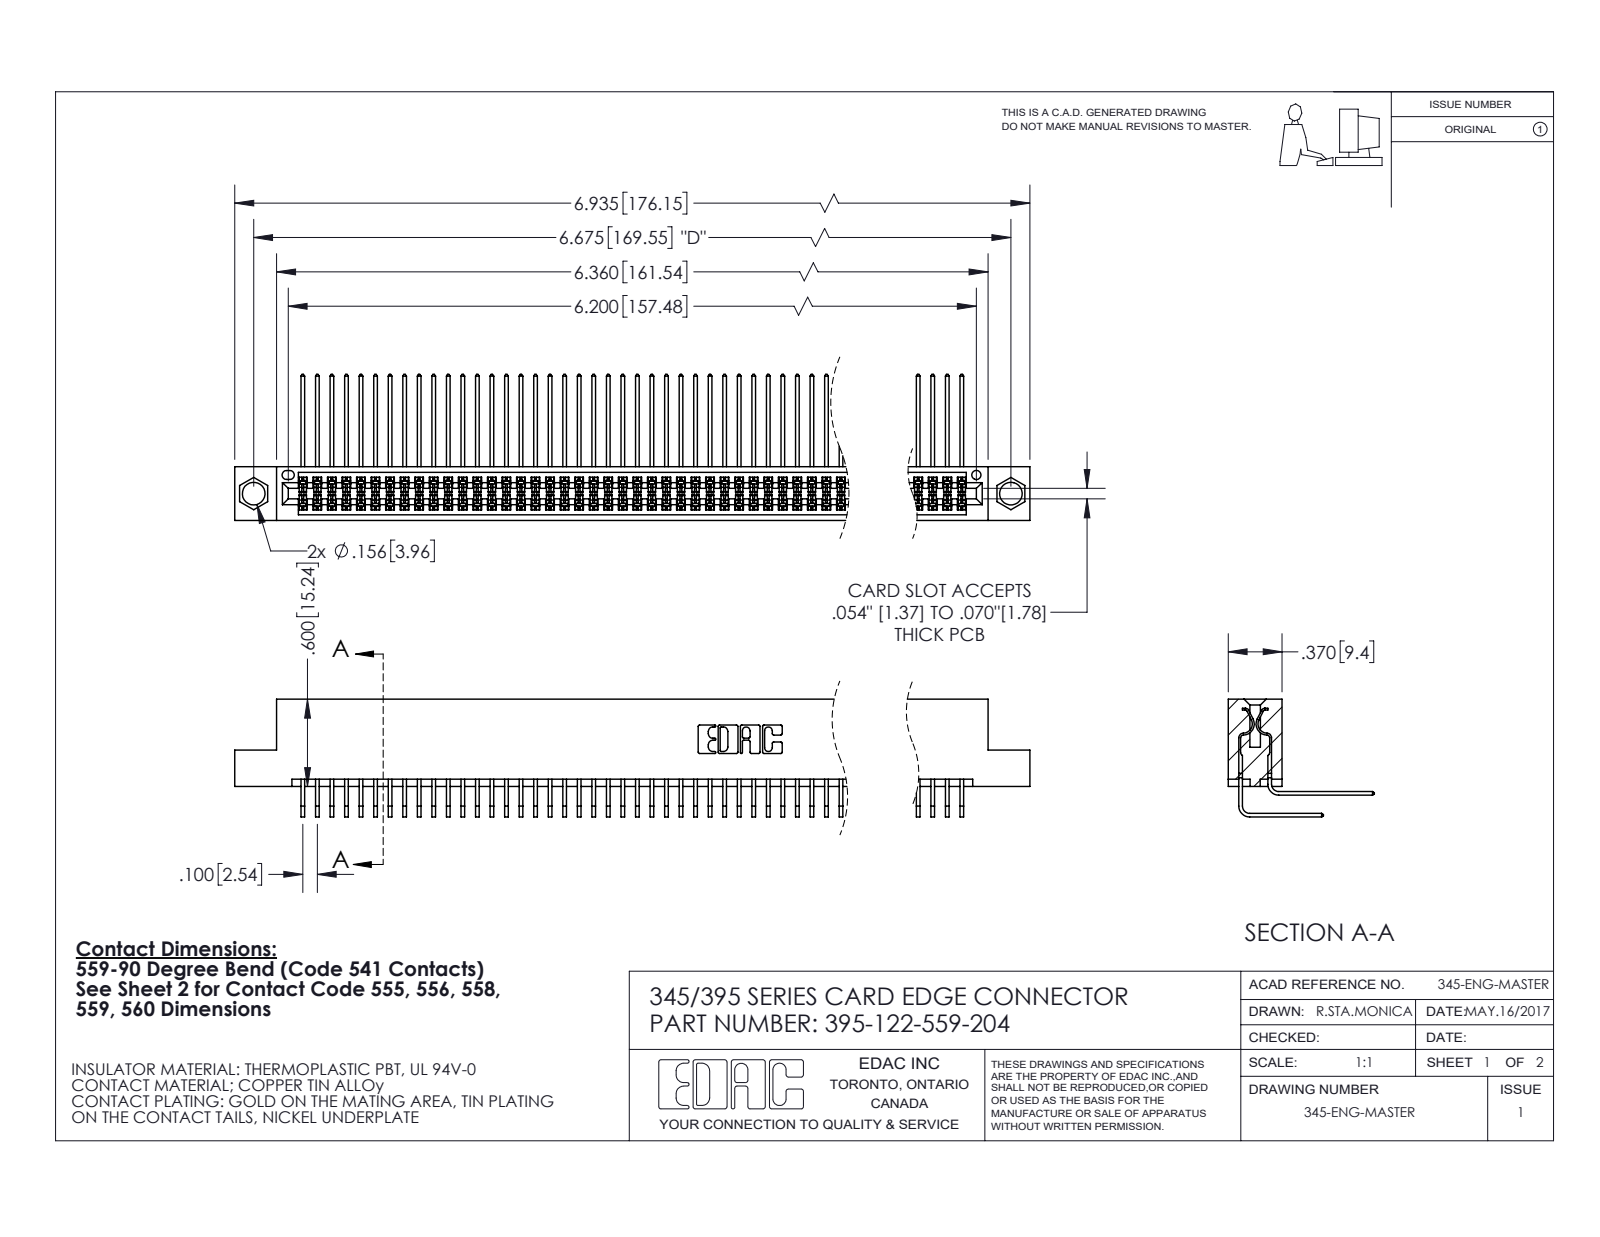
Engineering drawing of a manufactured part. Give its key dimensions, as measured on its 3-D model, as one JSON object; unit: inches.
{"part_name": "345-292-001_559 Tail - 2; 345 Part_Flush Mounting Lugs - 0.156 Dia-TI; 345-292-001_558 559 Tail - 1; 395-122-559-204", "step_written_by": "SolidWorks 2020 (CONFIG_CONTROL_DESIGN)", "units": "inches", "bodies": {"solids": 123, "faces": 6484, "planar": 4364, "cylindrical": 2120, "other": 0}, "overall_size": [6.935, 1.005, 0.809], "volume_in3": 1.091, "surface_area_in2": 46.45, "round_holes": [[0.156, 2], [0.064, 1]], "partial_cylinders_radius": [[0.006, 184], [0.01, 22], [0.007, 6], [0.031, 6], [0.026, 3], [0.014, 2], [0.019, 2], [0.022, 2]], "face_to_face_distances": [0.072, 0.298, 0.2, 0.37, 0.098, 0.272, 0.025, 0.225, 0.175, 0.15], "hole_center_spacings": [0.27, 6.439, 6.675]}
